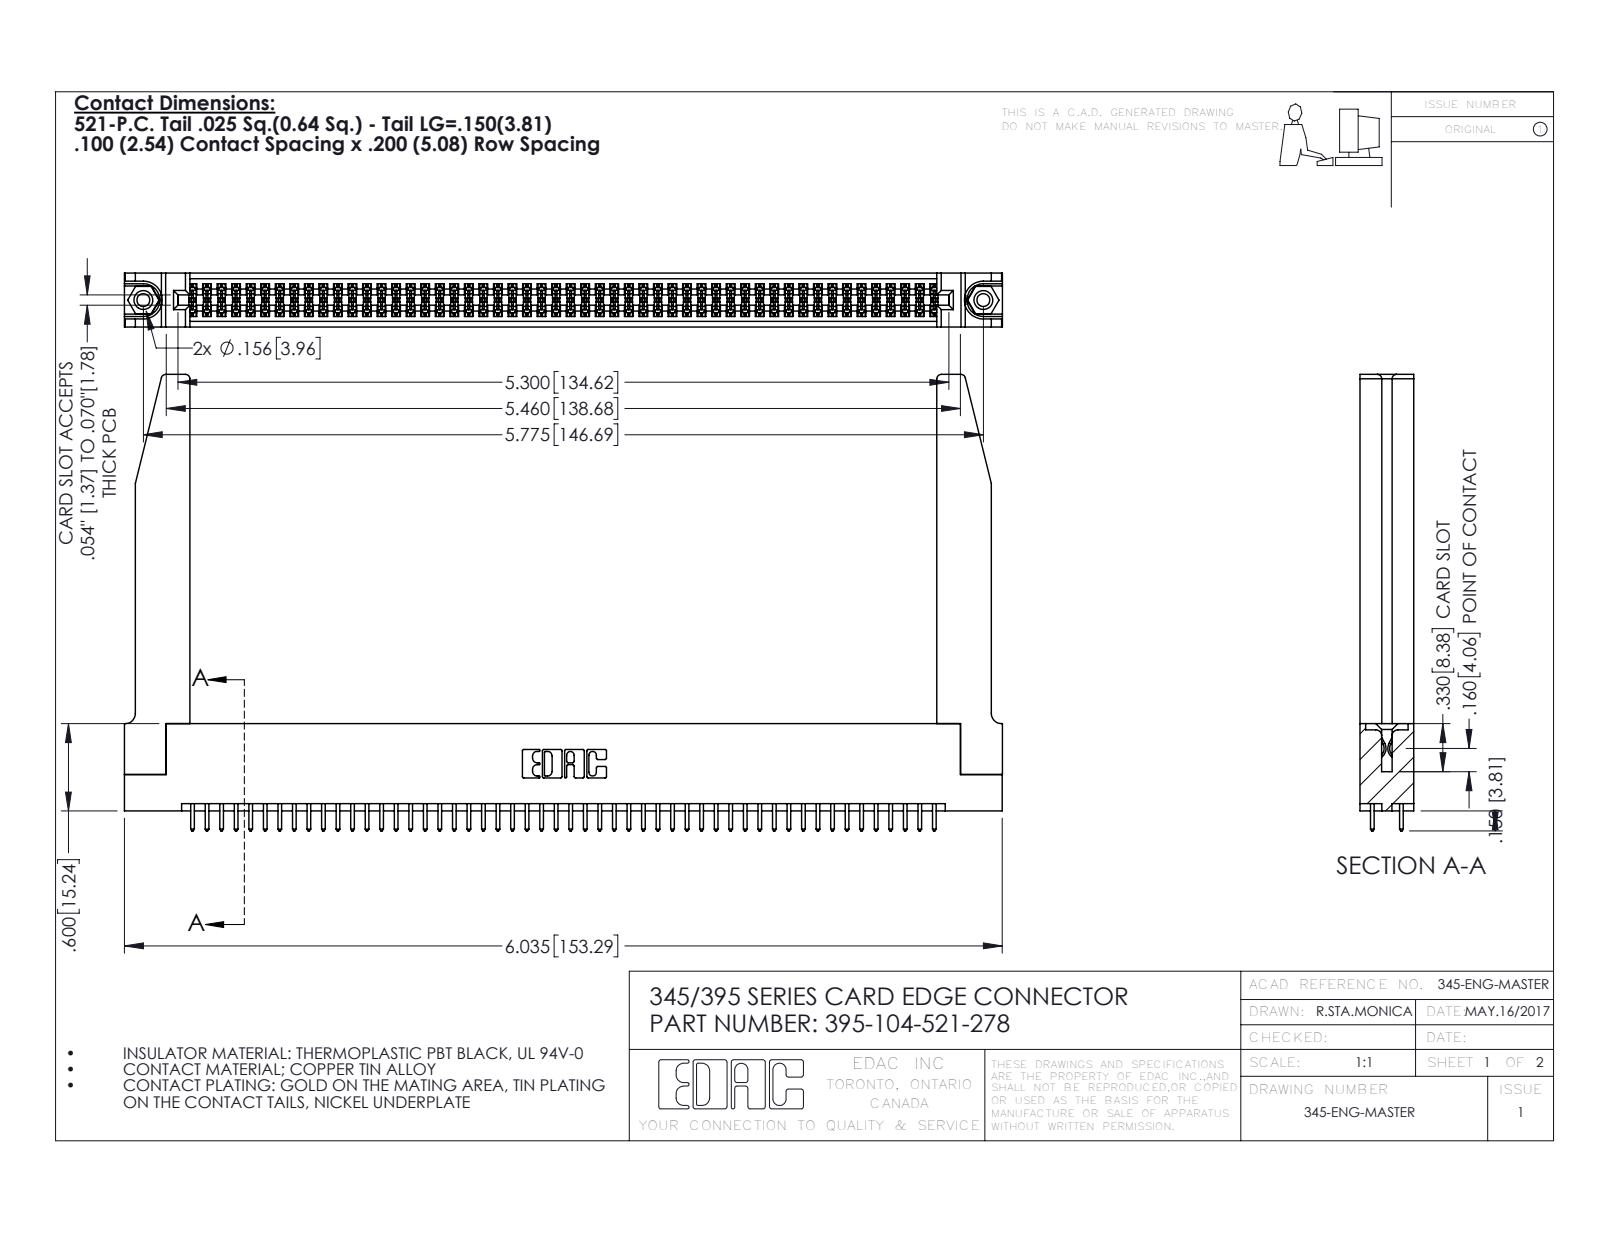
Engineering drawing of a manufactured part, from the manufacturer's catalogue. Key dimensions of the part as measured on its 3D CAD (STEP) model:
Part name (STEP PRODUCT): 345-220-078_345-220-078; 345-250-001_345-250-001-102; 395-104-521-278; 345-292-001_345-293-121 (+1 more)
STEP written by: SolidWorks 2016 (CONFIG_CONTROL_DESIGN)
Units: inches
Bodies: 109 solids, 5560 faces (3654 planar, 1854 cylindrical, 52 other)
Overall size (bounding box): 6.036 × 3.137 × 0.37
Volume: 1.386 in³ · Surface area: 44.71 in²
Round holes (diameter × count): ⌀0.089 ×2, ⌀0.125 ×2, ⌀0.156 ×2, ⌀0.064 ×1
Round bosses / shafts (diameter × count): ⌀0.155 ×2
Partial cylindrical surfaces — rounded edges, fillets, slot ends (radius × count): R0.006 ×156, R0.01 ×104, R0.01 ×22, R0.03 ×8, R0.007 ×6, R0.031 ×6, R0.026 ×3, R0.014 ×2
Main face-to-face distances: 0.072, 0.298, 0.37, 0.2, 0.098, 0.272, 0.025, 0.225, 0.175, 0.15
Hole centre spacings: 0.27, 5.539, 5.775
